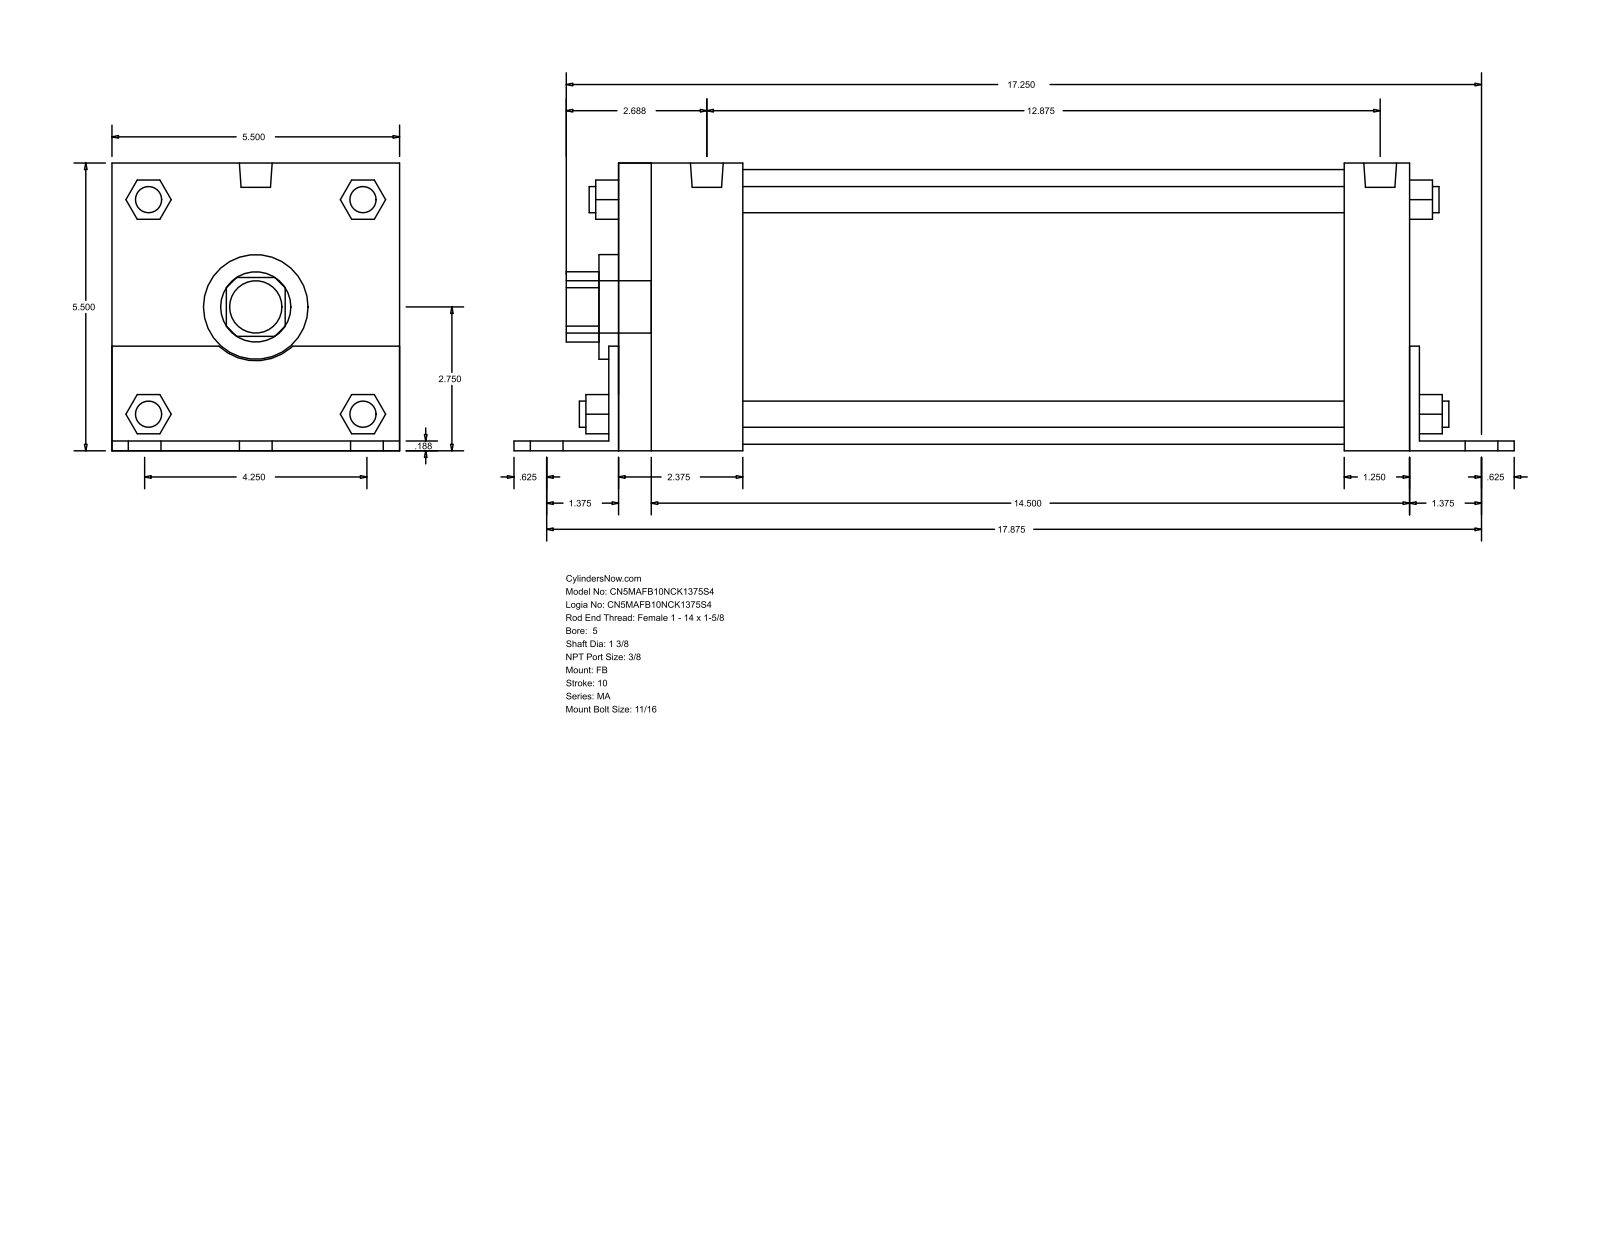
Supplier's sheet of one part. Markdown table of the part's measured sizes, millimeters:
| quantity | value |
| --- | --- |
| part name | MA_FB__0500_1.375 |
| STEP written by | GSSL Pune (CONFIG_CONTROL_DESIGN) |
| units | millimeters |
| bodies | 0 solids, 140 faces (105 planar, 35 cylindrical, 0 other) |
| overall size | 485.77 × 139.75 × 139.7 |
| round holes (diameter × count) | 34.92 × 1, 50.8 × 1, 133.35 × 1 |
| round bosses / shafts (diameter × count) | 17.46 × 6, 12.7 × 4, 11.11 × 4, 15.93 × 2, 25.4 × 1 |
| partial cylindrical surfaces (radius × count) | 17.06 × 1, 26.16 × 1 |
| main face-to-face distances | 139.7, 4.76, 139.75, 4.71, 134.99, 384.17, 4.77, 388.94, 388.93, 393.7 |
